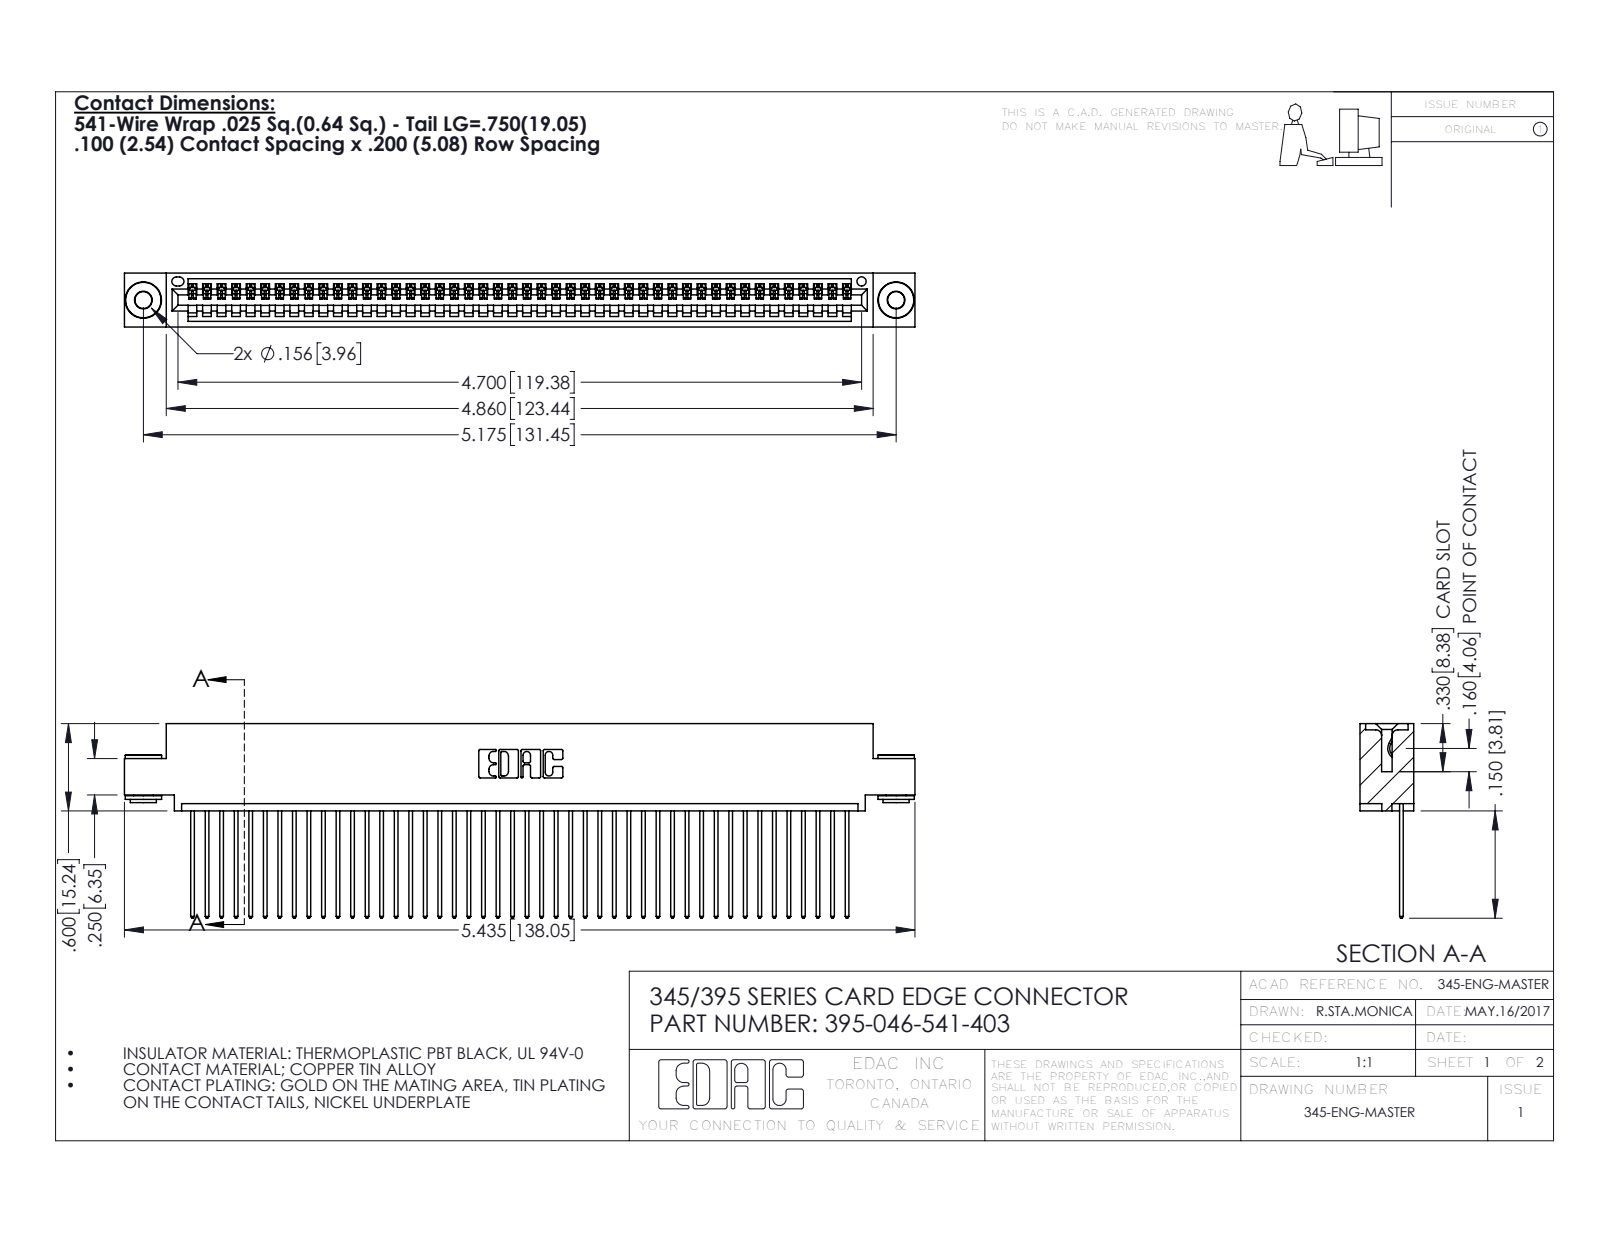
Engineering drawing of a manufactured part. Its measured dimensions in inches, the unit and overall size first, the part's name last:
Units: inches
Overall size (bounding box): 5.435 × 1.337 × 0.37
Round holes (diameter × count): ⌀0.116 ×2, ⌀0.156 ×2, ⌀0.064 ×1
Round bosses / shafts (diameter × count): ⌀0.25 ×2, ⌀0.18 ×2, ⌀0.136 ×2
Partial cylindrical surfaces — rounded edges, fillets, slot ends (radius × count): R0.006 ×92, R0.01 ×92, R0.01 ×22, R0.007 ×6, R0.031 ×6, R0.026 ×3, R0.031 ×2, R0.04 ×2
Main face-to-face distances: 0.072, 0.298, 0.025, 0.098, 0.272, 0.37, 0.2, 0.225, 0.149, 0.072
Hole centre spacings: 0.27, 4.939, 5.175
Volume: 0.808 in³ · Surface area: 29.21 in²
Bodies: 49 solids, 2836 faces (1934 planar, 894 cylindrical, 8 other)
Part name (STEP PRODUCT): 395-046-541-403; 345-292-001_345-293-141; 345 Part_0.110 Offset - 0.156 Dia-TH; 345-250-002_345-250-002-102
STEP written by: SolidWorks 2016 (CONFIG_CONTROL_DESIGN)
